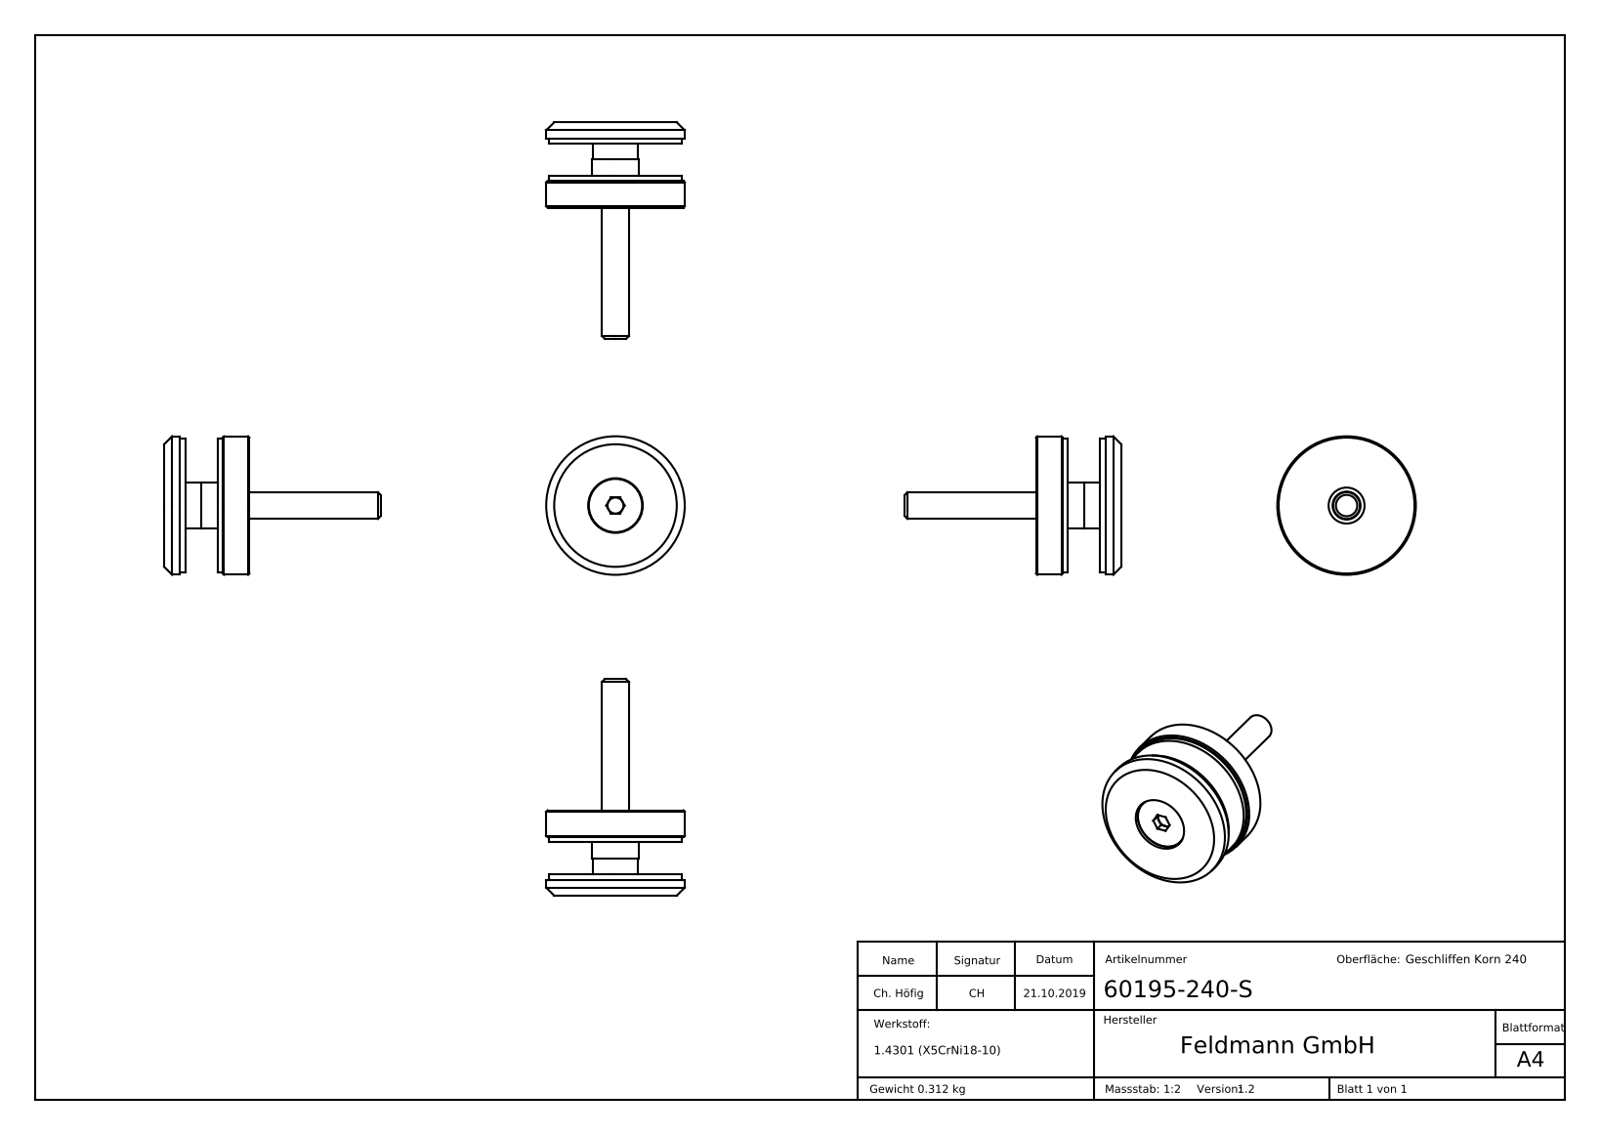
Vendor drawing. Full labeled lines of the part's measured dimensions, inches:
Part name (STEP PRODUCT): DIN7991 M10x80; 60195-240-S Teil4; 60195-240-S Teil3_60195-240-S Teil3; 60195-240-S Teil3 (+8 more)
STEP written by: SolidWorks 2015 (CONFIG_CONTROL_DESIGN)
Units: inches
Bodies: 6 solids, 294 faces (154 planar, 15 cylindrical, 125 other)
Overall size (bounding box): 3.199 × 2.047 × 2.047
Volume: 2.862 in³ · Surface area: 37.39 in²
Round holes (diameter × count): ⌀0.413 ×1, ⌀0.551 ×1, ⌀0.807 ×1
Round bosses / shafts (diameter × count): ⌀2.047 ×1, ⌀1.969 ×1, ⌀0.787 ×1, ⌀0.689 ×1, ⌀0.669 ×1, ⌀0.394 ×1
Main face-to-face distances: 0.551, 0.079, 0.63, 0.472, 0.236, 0.394, 1.024, 0.315, 0.945, 1.26
